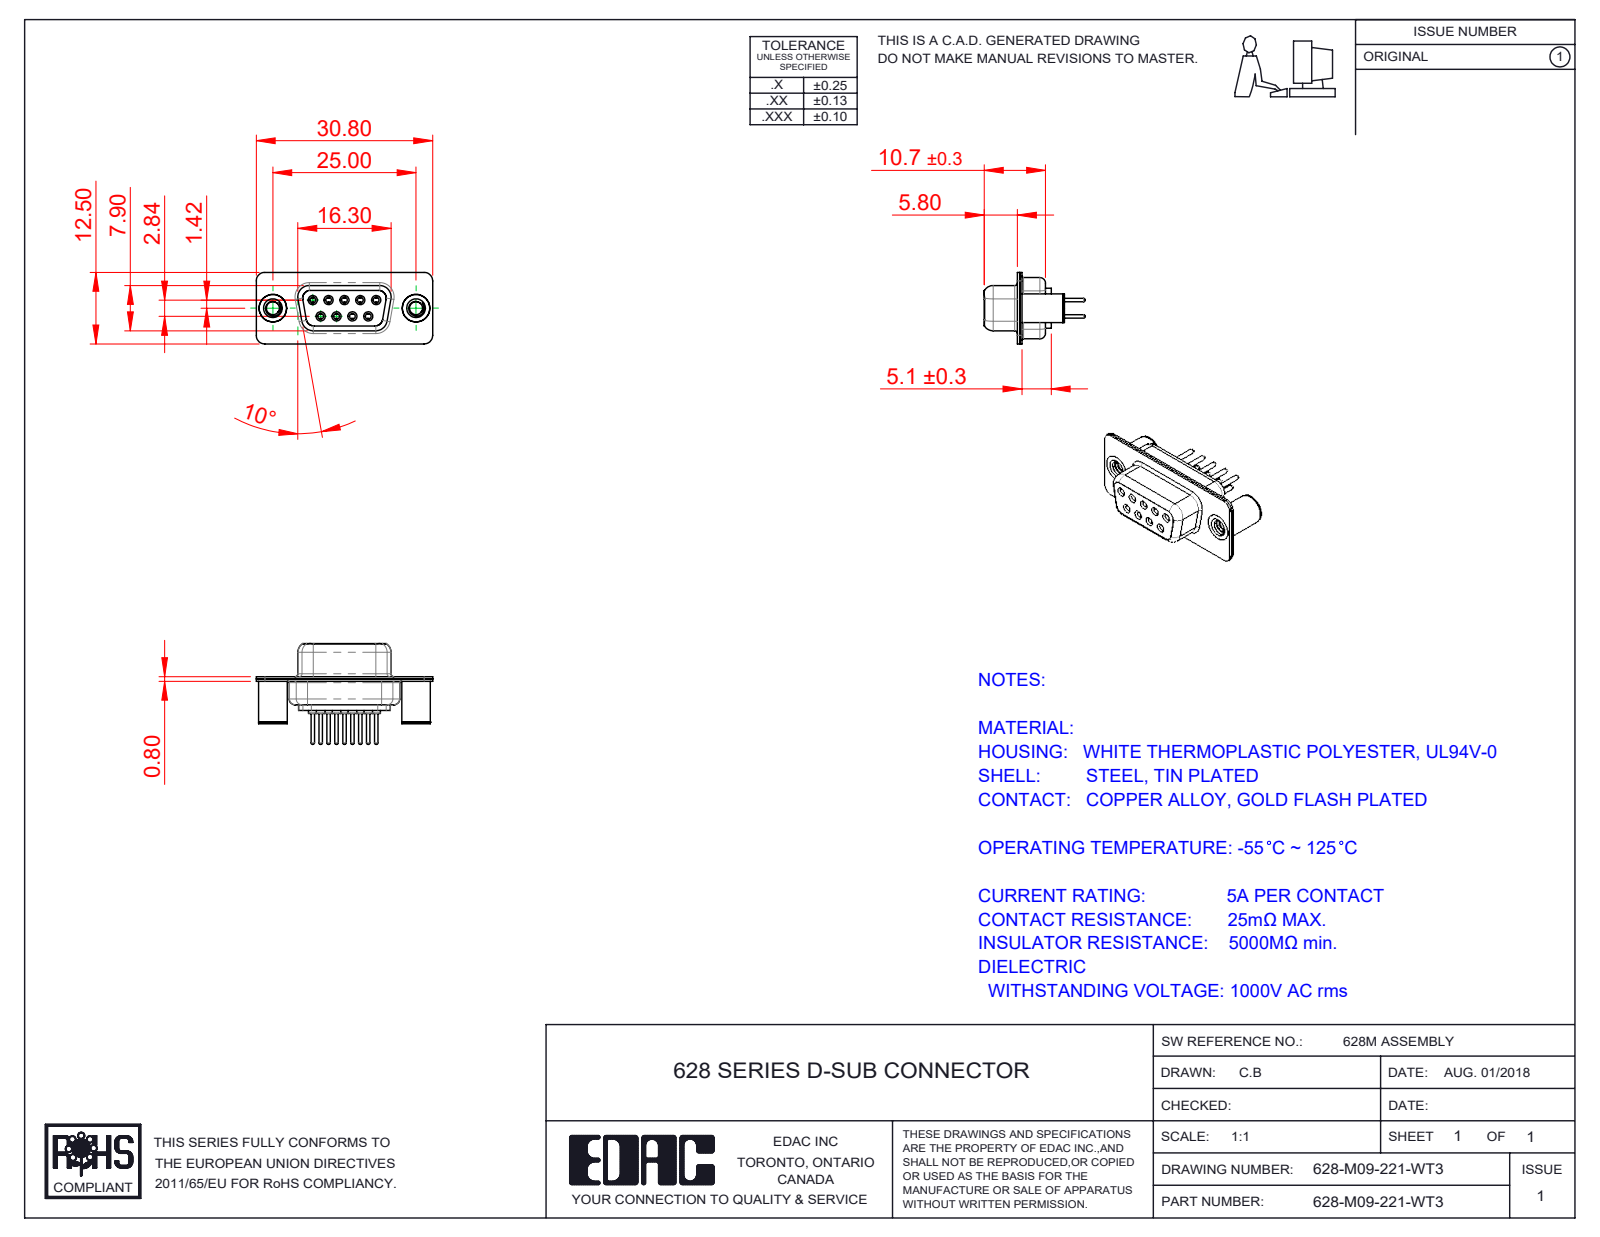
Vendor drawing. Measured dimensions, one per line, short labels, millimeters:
name: 628-M09-221-WT3; 628M Shell Front_09 Contacts; 628M Contact Row 2_21; 628M Shell Rear_09 Contacts (+3 more)
written by: SolidWorks 2020 (CONFIG_CONTROL_DESIGN)
unit: mm
bodies: 14 solids, 808 faces (202 planar, 332 cylindrical, 274 other)
size: 30.8 × 17.6 × 12.5
volume: 1 825 mm³; area: 4 681 mm²
holes: 9× ⌀1, 9× ⌀1.1, 9× ⌀1.7, 9× ⌀1.8, 9× ⌀2, 2× ⌀2.26, 2× ⌀3.26, 2× ⌀4, 2× ⌀4.8
bosses: 9× ⌀2.2, 9× ⌀1.6, 9× ⌀1.5, 9× ⌀0.6, 2× ⌀5, 2× ⌀4.9
rounds: 16× R1.5, 12× R2, 8× R1.35, 8× R1.6, 4× R0.25, 4× R0.5, 4× R0.6, 4× R0.65
face distances: 0.4, 1.4, 0.45, 8.45, 0.8, 1.8, 8.9, 1, 6.2, 7.05
hole spacings: 3.16, 2.77, 5.54, 5.03, 5.04, 8.31, 7.1, 7.48
